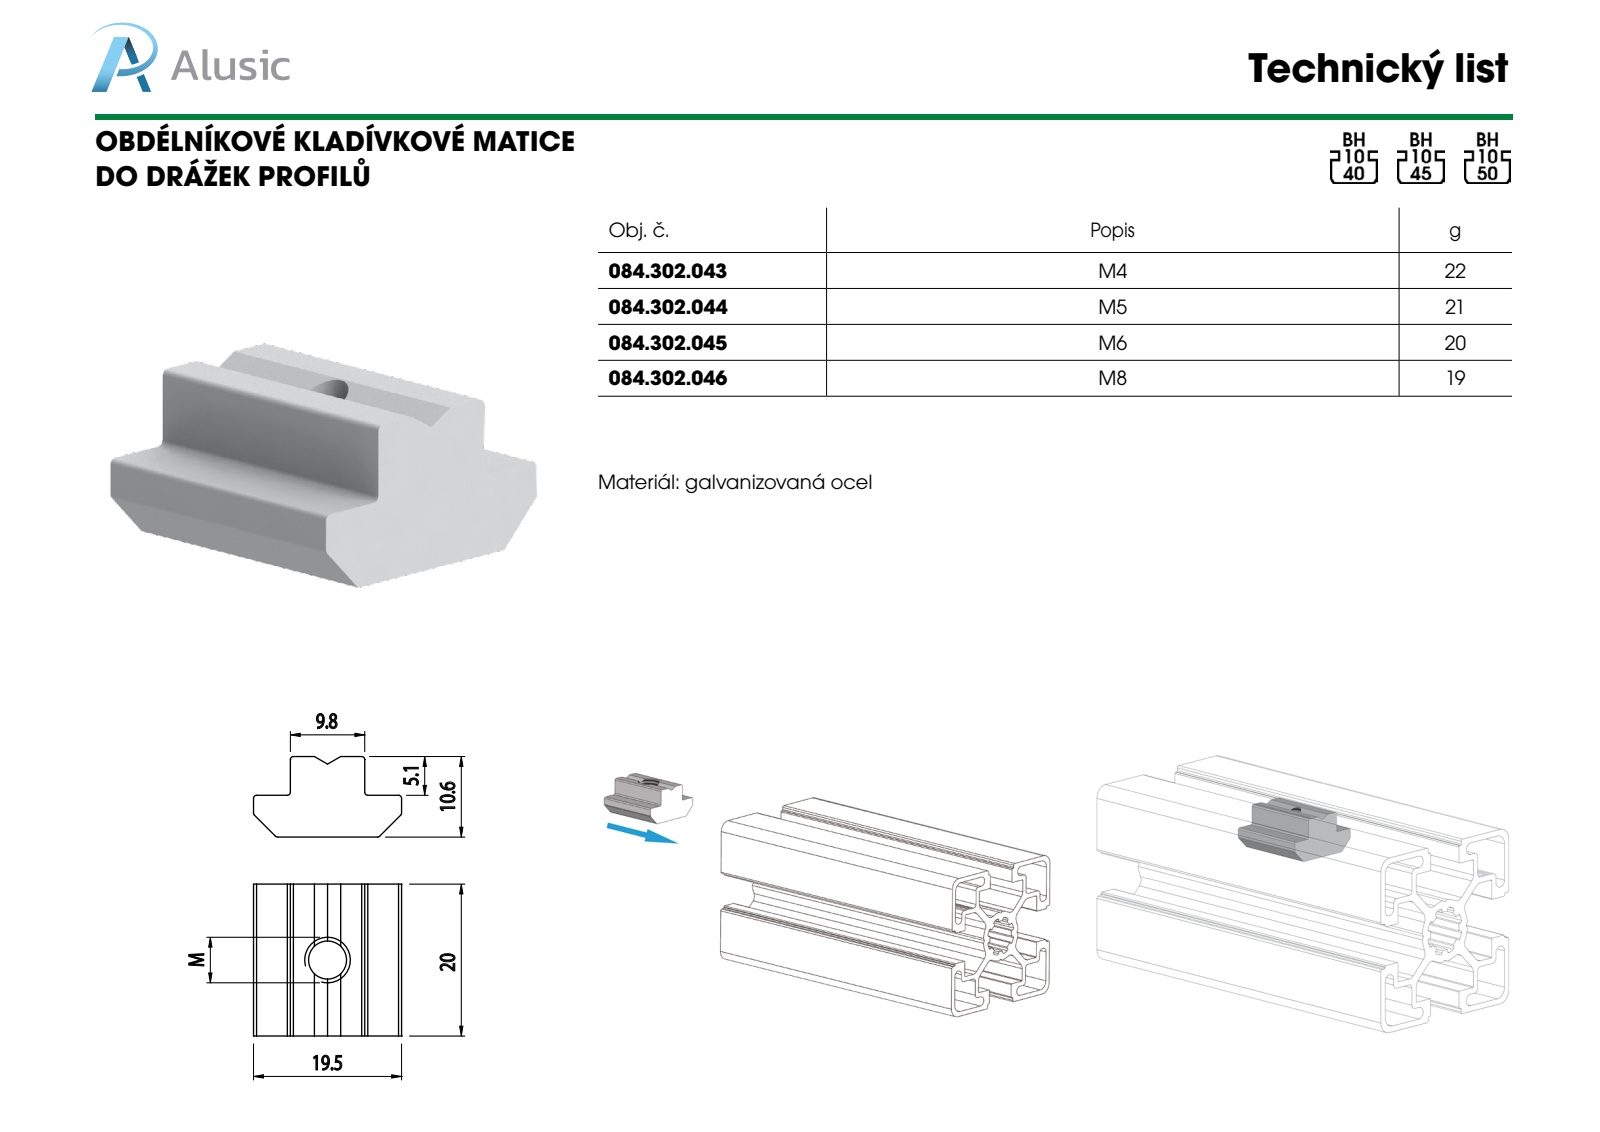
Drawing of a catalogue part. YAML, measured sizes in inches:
part_name: "084.302.043"
step_written_by: "SolidWorks 2011 (CONFIG_CONTROL_DESIGN)"
units: inches
bodies: {solids: 1, faces: 27, planar: 15, cylindrical: 12, other: 0}
overall_size: [0.787, 0.768, 0.417]
volume: 0.173
surface_area: 2.33
round_holes:
  - {diameter: 0.13, count: 1}
partial_cylinders:
  - {radius: 0.016, count: 10}
face_to_face_distances: [0.217, 0.787, 0.417, 0.201, 0.386, 0.191, 0.577, 0.768]
